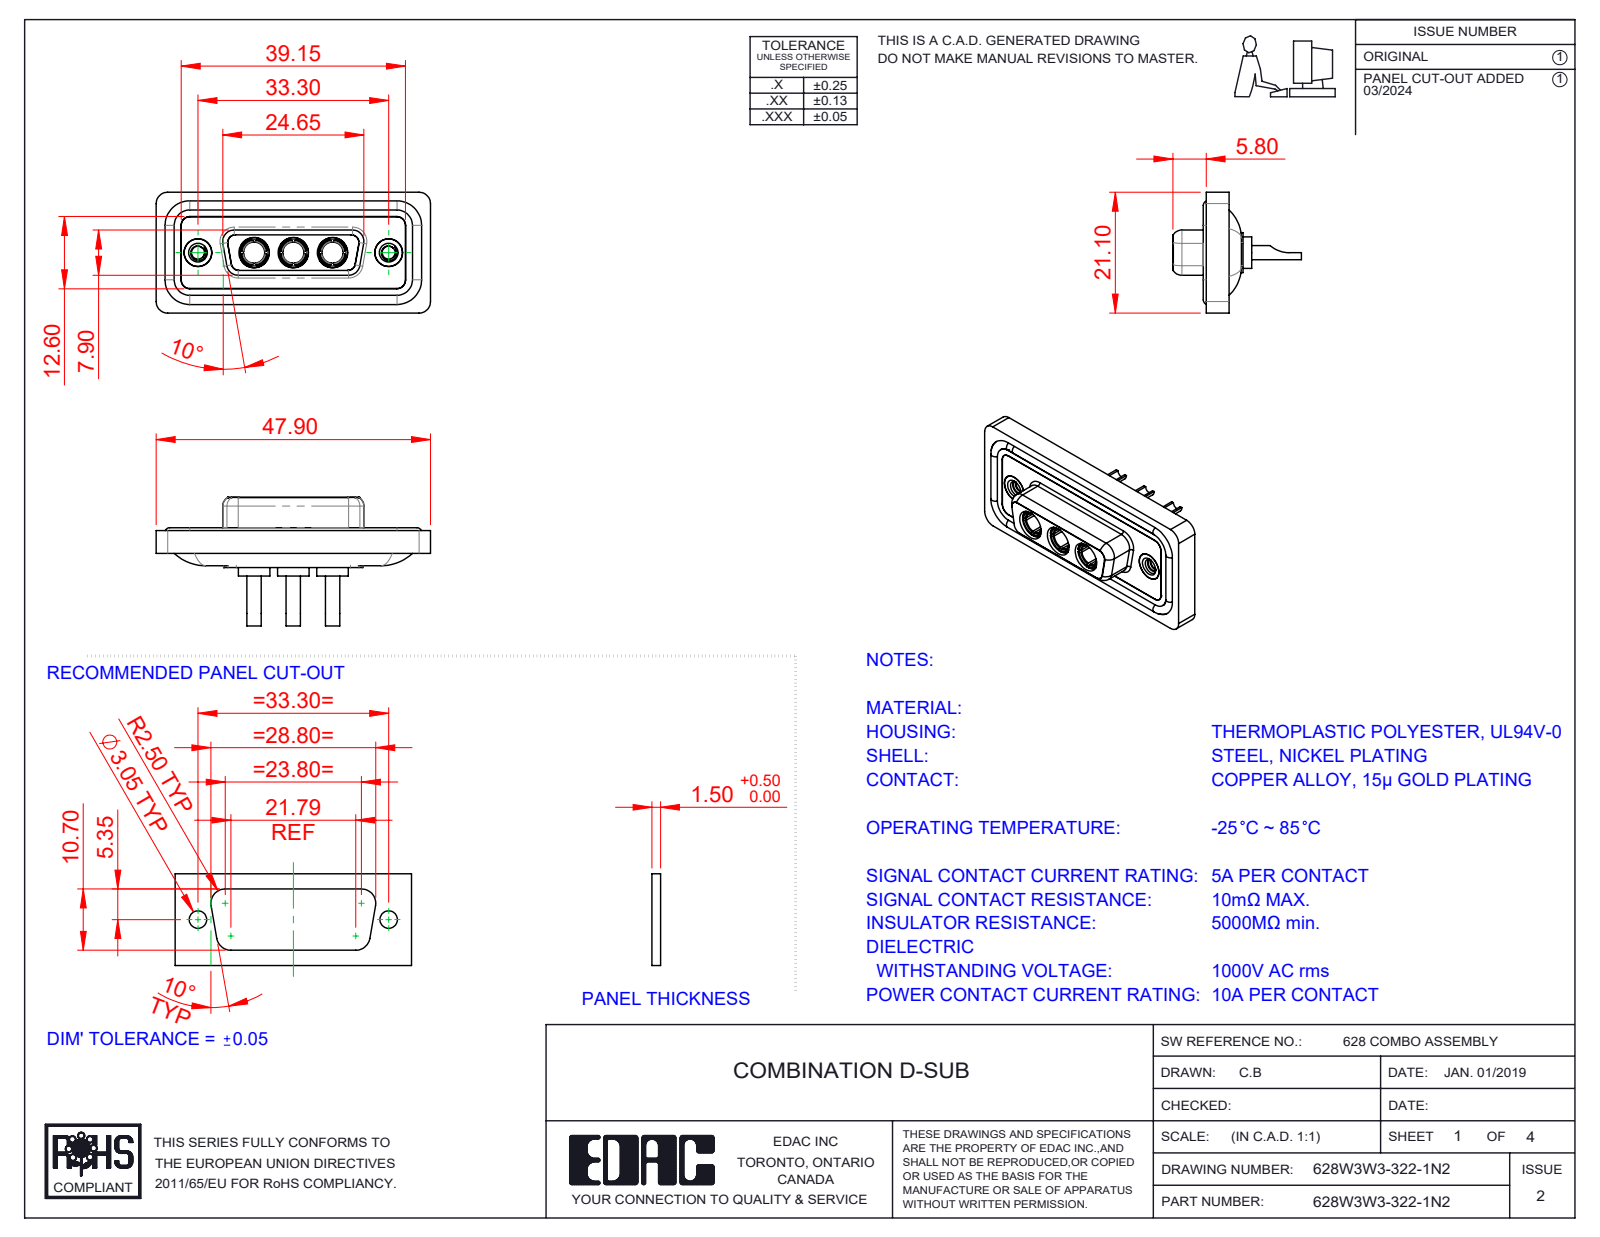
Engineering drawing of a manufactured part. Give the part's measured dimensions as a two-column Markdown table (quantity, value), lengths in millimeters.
| quantity | value |
| --- | --- |
| part name | 628Combo Threaded Rivet_2; 628Combo Shell Front_15 Contacts; 628W3W3-322-1N2; 628Combo Shell Rear_15 Contacts (+3 more) |
| STEP written by | SolidWorks 2023 (CONFIG_CONTROL_DESIGN) |
| units | millimeters |
| bodies | 13 solids, 623 faces (198 planar, 266 cylindrical, 159 other) |
| overall size | 47.9 × 22.45 × 21.1 |
| volume | 6 018 mm³ |
| surface area | 9 882 mm² |
| round holes (diameter × count) | 4.85 × 5, 1.7 × 3, 3.7 × 3, 5.3 × 3, 2.26 × 2, 4 × 2, 4.05 × 2, 5 × 2 |
| round bosses / shafts (diameter × count) | 1.6 × 4, 5.5 × 3, 5.2 × 3, 4.96 × 3, 4.75 × 3, 3.75 × 3, 2.5 × 3, 4.95 × 2 |
| partial cylindrical surfaces (radius × count) | 1.5 × 22, 2 × 20, 1.35 × 12, 1.6 × 8, 0.25 × 4, 0.5 × 4, 0.6 × 4, 0.65 × 4 |
| main face-to-face distances | 0.4, 1.8, 1.6, 0.5, 7.45, 1.1, 2.9, 5.65, 7.05, 6.6 |
| hole center spacings | 6.85, 9.8, 16.65, 23.5, 13.7, 33.3 |
